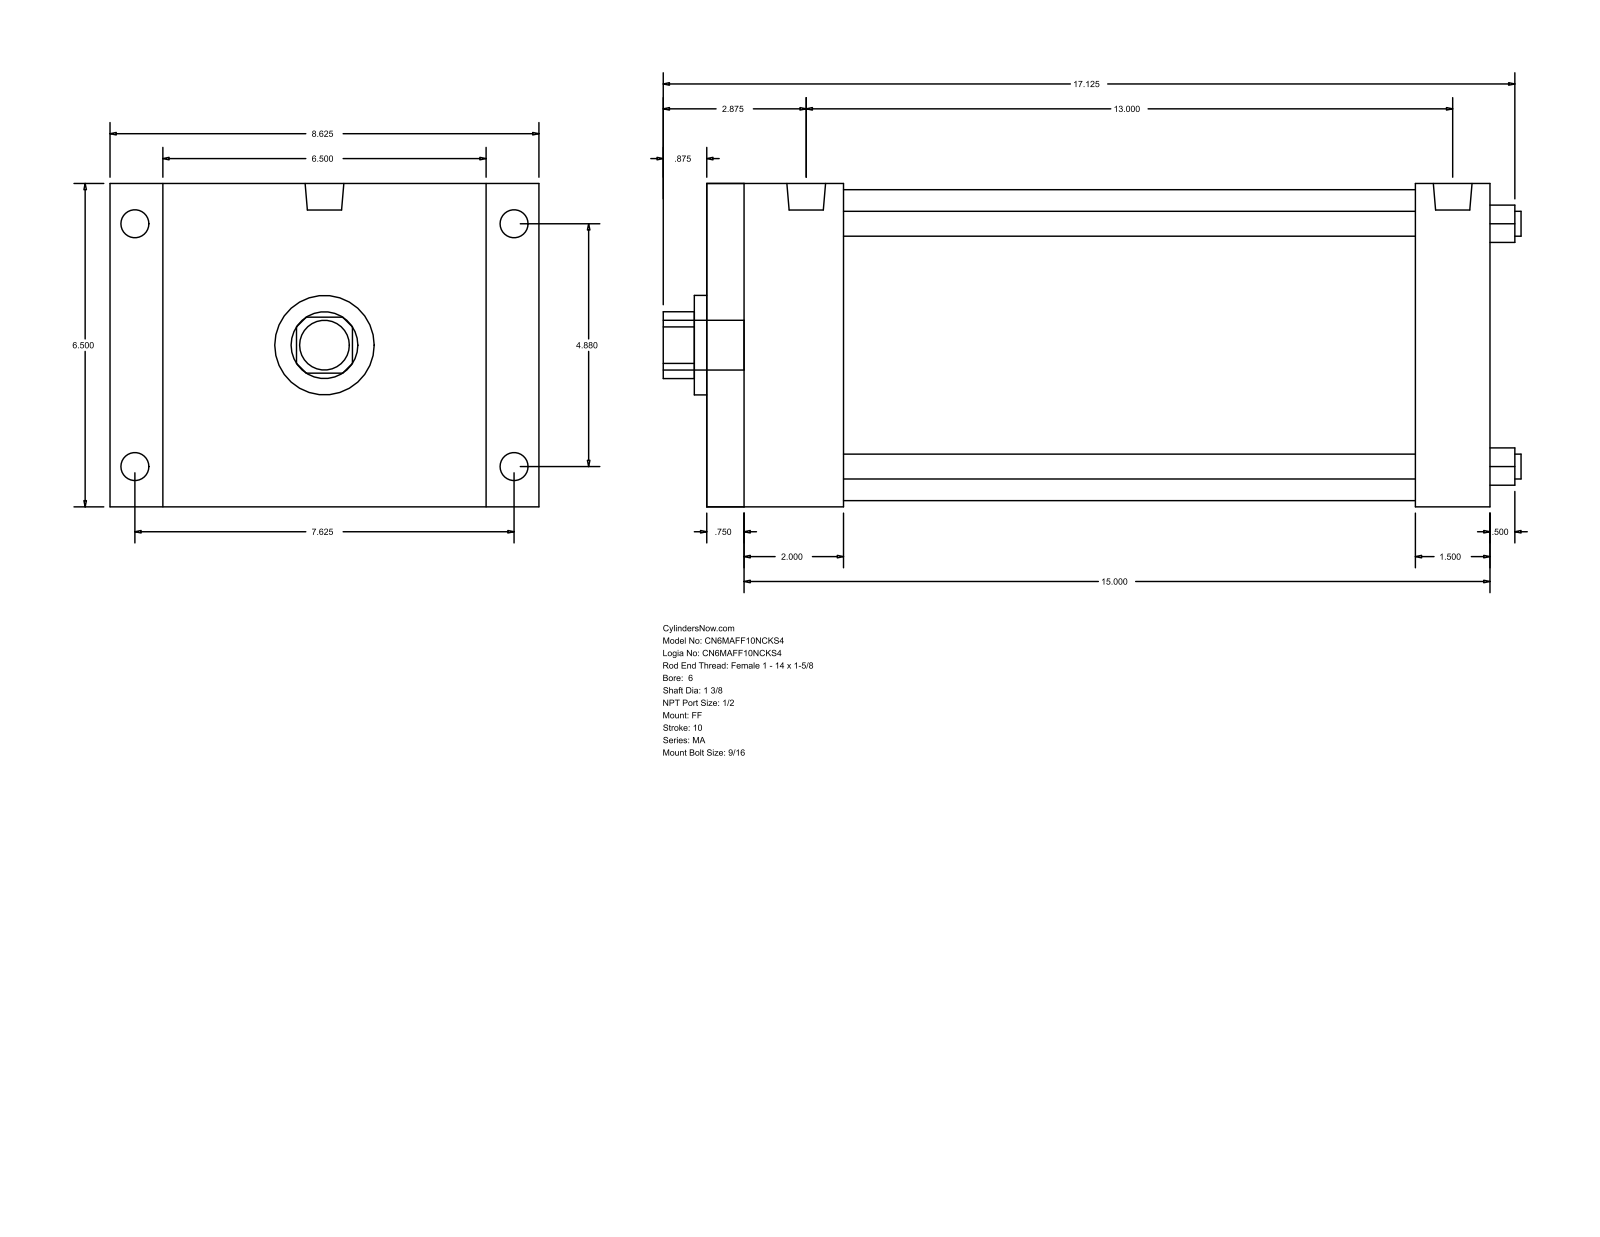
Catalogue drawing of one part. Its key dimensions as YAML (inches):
part_name: "MA_FF__0600_1.375"
step_written_by: "GSSL Pune (CONFIG_CONTROL_DESIGN)"
units: inches
bodies: {solids: 0, faces: 92, planar: 64, cylindrical: 28, other: 0}
overall_size: [17.25, 8.625, 6.5]
round_holes:
  - {diameter: 0.5, count: 4}
  - {diameter: 1.375, count: 1}
  - {diameter: 2, count: 1}
  - {diameter: 6.25, count: 1}
round_bosses_or_shafts:
  - {diameter: 0.687, count: 4}
  - {diameter: 0.563, count: 4}
  - {diameter: 0.778, count: 2}
  - {diameter: 1, count: 1}
partial_cylinders:
  - {radius: 0.672, count: 1}
face_to_face_distances: [6.5, 15.75, 0.625, 15.125, 2, 13.625, 2.625, 13.125, 14.25, 11.625]
hole_center_spacings: [3.451, 4.88, 6.902]
